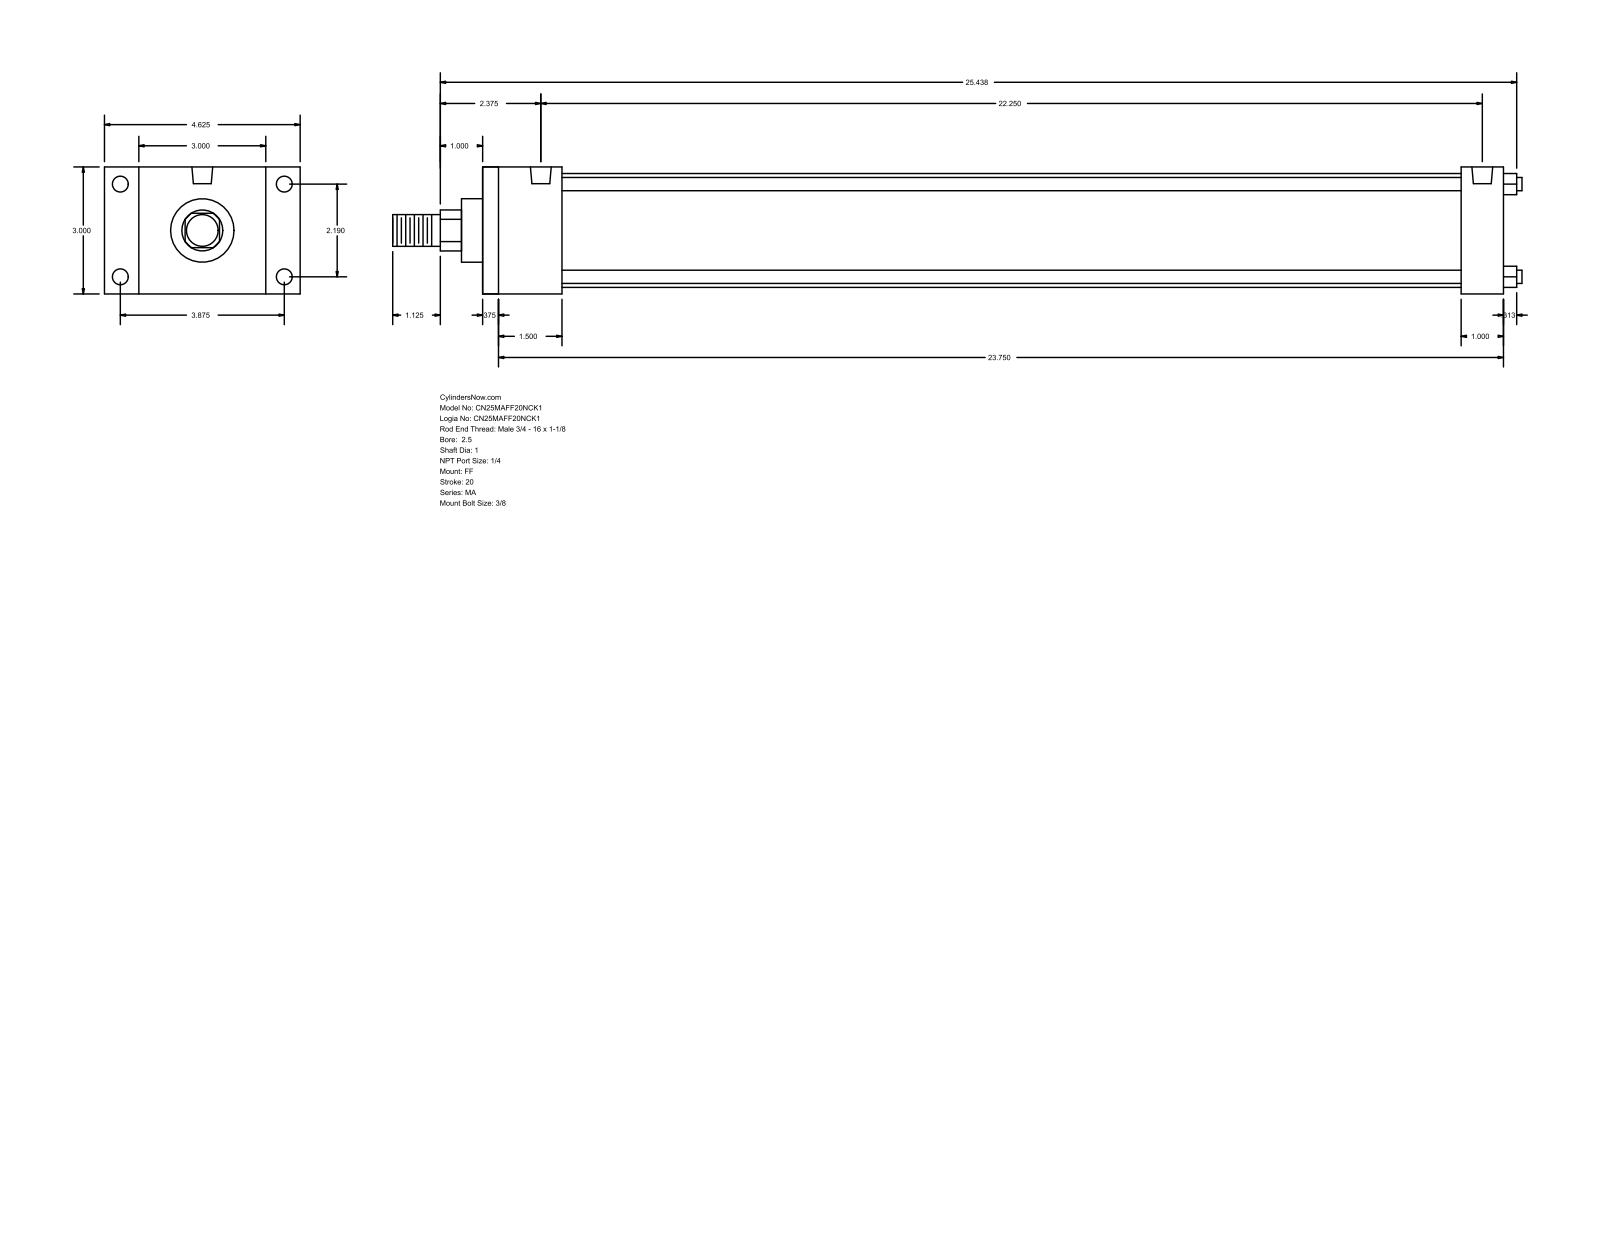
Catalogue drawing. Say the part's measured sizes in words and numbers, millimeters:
The part is named "MA_FF__0250_1". Its 3-D file was written by "GSSL Pune (CONFIG_CONTROL_DESIGN)". It is 0 solids with 92 faces: 64 planar, 28 cylindrical and 0 other. Overall it measures 677.86 by 117.47 by 76.2 millimeters. Round holes: 4 of diameter 7.94, 4 of diameter 9.53, 2 of diameter 12.49. Round bosses or shafts: 4 of diameter 7.94, 1 of diameter 68.33, 1 of diameter 38.1, 1 of diameter 25.4, 1 of diameter 19.05. Partial cylindrical surfaces (rounded edges, fillets, slot ends): 1 of radius 12.29. The main face-to-face distances are 76.2, 612.77, 9.52, 603.25, 25.4, 47.63, 587.37, 38.11, 577.85, 539.74. The hole center spacings are 55.62, 98.42, 113.05, 565.15.
